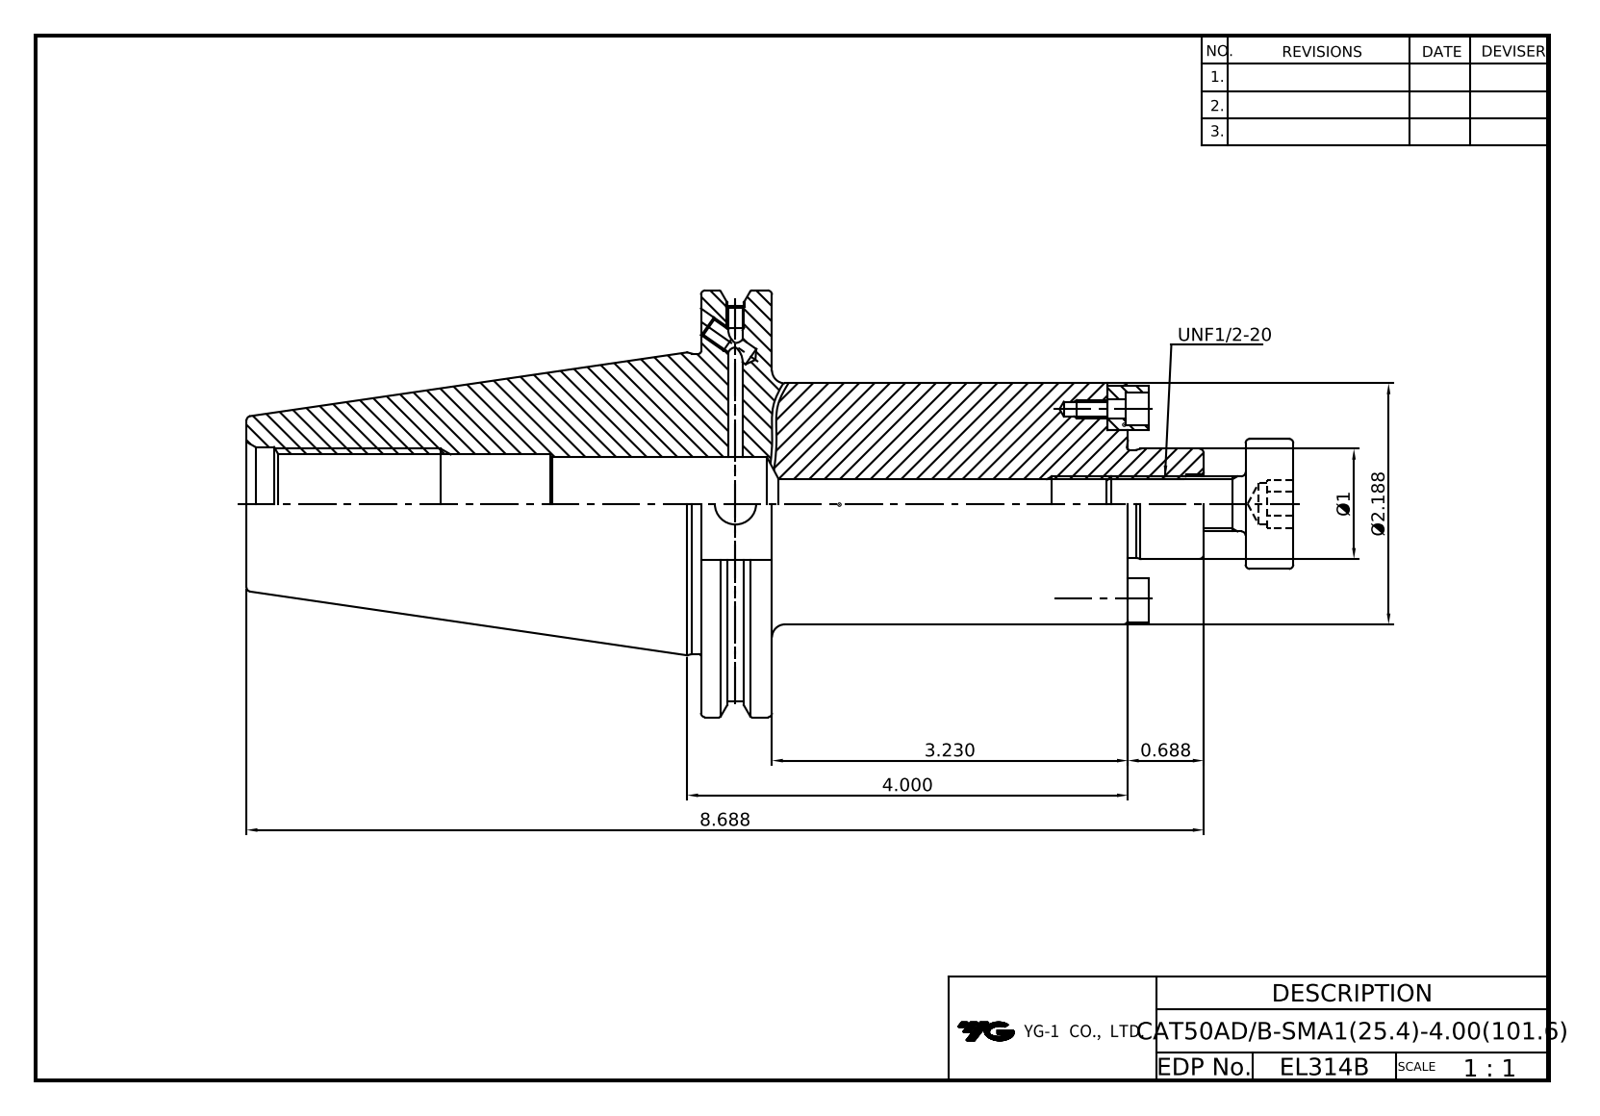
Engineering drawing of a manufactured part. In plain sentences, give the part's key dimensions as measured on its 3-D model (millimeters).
The part is named "CAT50ADB-SMA25.4-4.00(20231027); CAT50ADB-SMA25.4C-4.00(20231027); DRIVE KEY-9.52x9.52x10.2; COLLAR BOLT-UNF1_2-20x32L". Its 3-D file was written by "Autodesk Inventor 2024 (AUTOMOTIVE_DESIGN)". It is 4 solids with 144 faces: 70 planar, 41 cylindrical and 33 other. Overall it measures 235.32 by 98.42 by 94.69 millimeters. Its volume is 520 849 cubic millimeters and its surface area 70 671 square millimeters. Round holes: 2 of diameter 3.24, 2 of diameter 3.3, 2 of diameter 4.13, 2 of diameter 4.2, 2 of diameter 4.5, 2 of diameter 5, 2 of diameter 7.5, 2 of diameter 9.53, 1 of diameter 11.33, 1 of diameter 13.5, 1 of diameter 21.5, 1 of diameter 21.97. Round bosses or shafts: 1 of diameter 98.42, 1 of diameter 91.29, 1 of diameter 69.25, 1 of diameter 55.58, 1 of diameter 30, 1 of diameter 25.4, 1 of diameter 24.9, 1 of diameter 12.7. Partial cylindrical surfaces (rounded edges, fillets, slot ends): 2 of radius 4.76. The main face-to-face distances are 15.88, 98.43, 82.55, 130.55, 114.67, 32.12, 104.77, 120.65, 203.2, 235.32. The hole center spacings are 21.85, 43.7.
